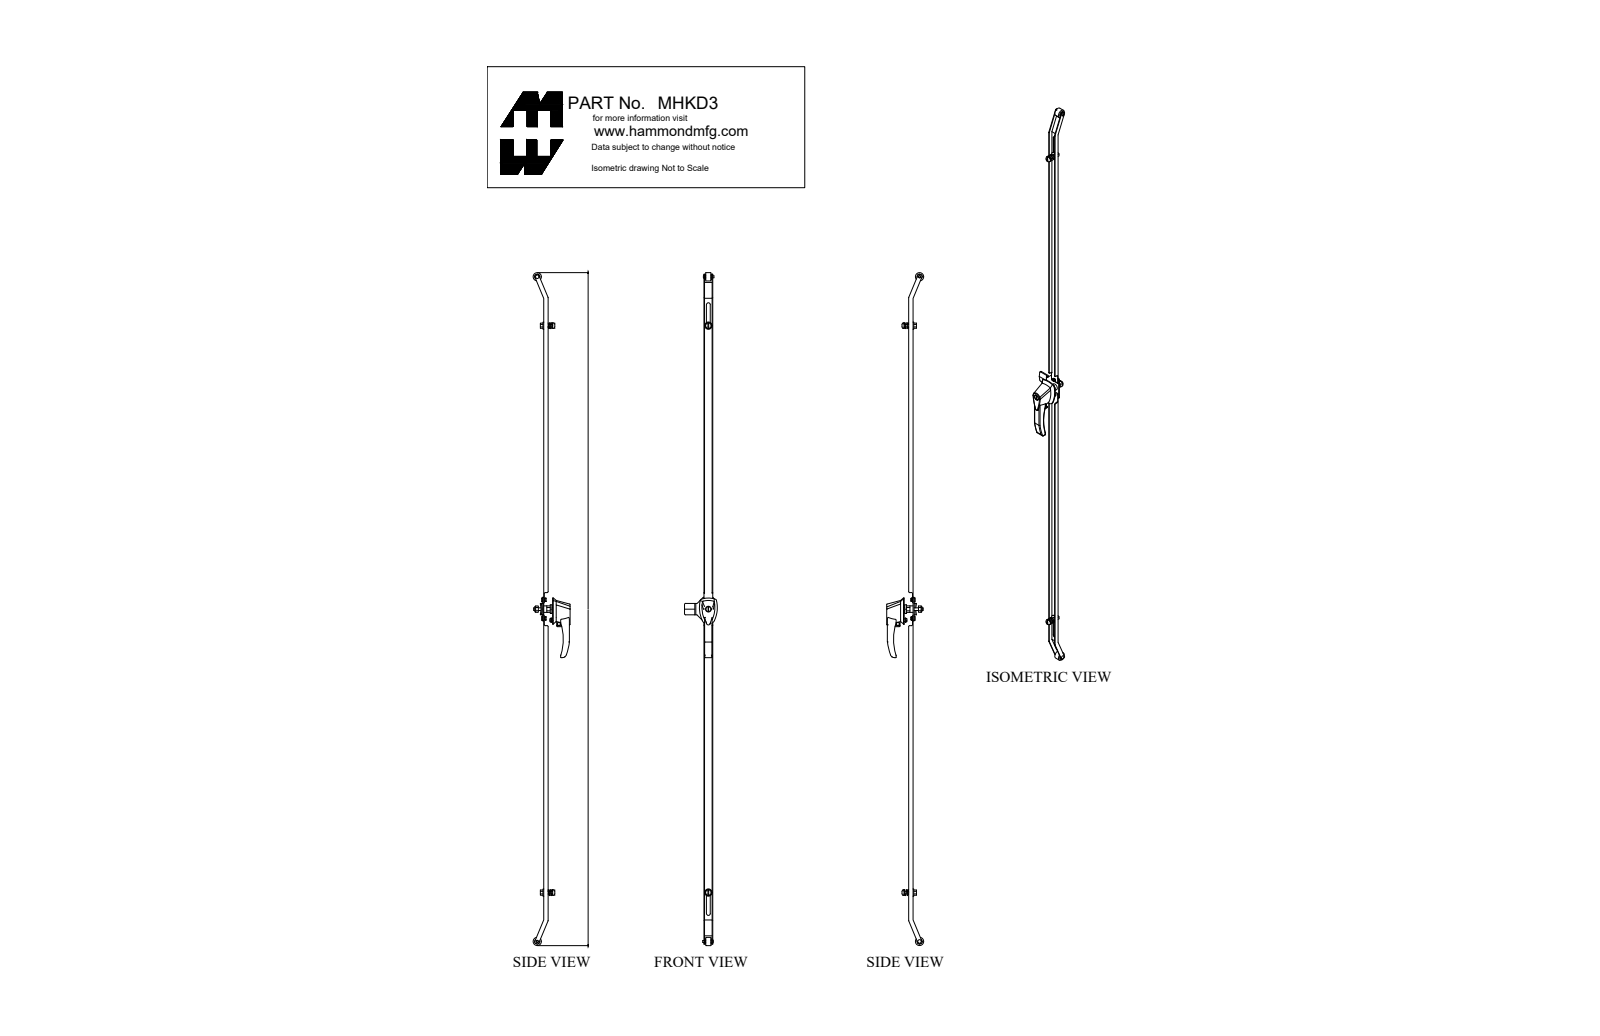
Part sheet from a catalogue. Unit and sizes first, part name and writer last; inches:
Units: inches
Overall size (bounding box): 81.493 × 4.473 × 3.975
Round holes (diameter × count): ⌀0.375 ×3, ⌀0.159 ×2, ⌀0.195 ×2, ⌀0.25 ×2, ⌀0.257 ×2, ⌀0.28 ×2, ⌀0.281 ×2, ⌀0.307 ×2, ⌀0.39 ×2, ⌀0.413 ×2, ⌀0.173 ×1, ⌀0.233 ×1
Round bosses / shafts (diameter × count): ⌀1 ×2, ⌀0.882 ×2, ⌀0.678 ×2, ⌀0.63 ×2, ⌀0.402 ×2, ⌀0.325 ×2, ⌀0.278 ×2, ⌀0.18 ×2
Partial cylindrical surfaces — rounded edges, fillets, slot ends (radius × count): R0.125 ×22, R0.03 ×6, R0.06 ×6, R0.09 ×6, R0.01 ×4, R0.234 ×4, R0.312 ×2, R0.75 ×2
Main face-to-face distances: 0.07, 0.992, 1.062, 0.922, 0.531, 0.461, 0.076, 0.986, 0.916, 1.077
Hole centre spacings: 1.126, 1.287, 33.202, 34.327, 34.333, 35.453, 0.213, 0.625
Volume: 24.41 in³ · Surface area: 416.6 in²
Bodies: 32 solids, 546 faces (271 planar, 212 cylindrical, 63 other)
Part name (STEP PRODUCT): MHKD3
STEP written by: SolidWorks 2018 (AUTOMOTIVE_DESIGN)
